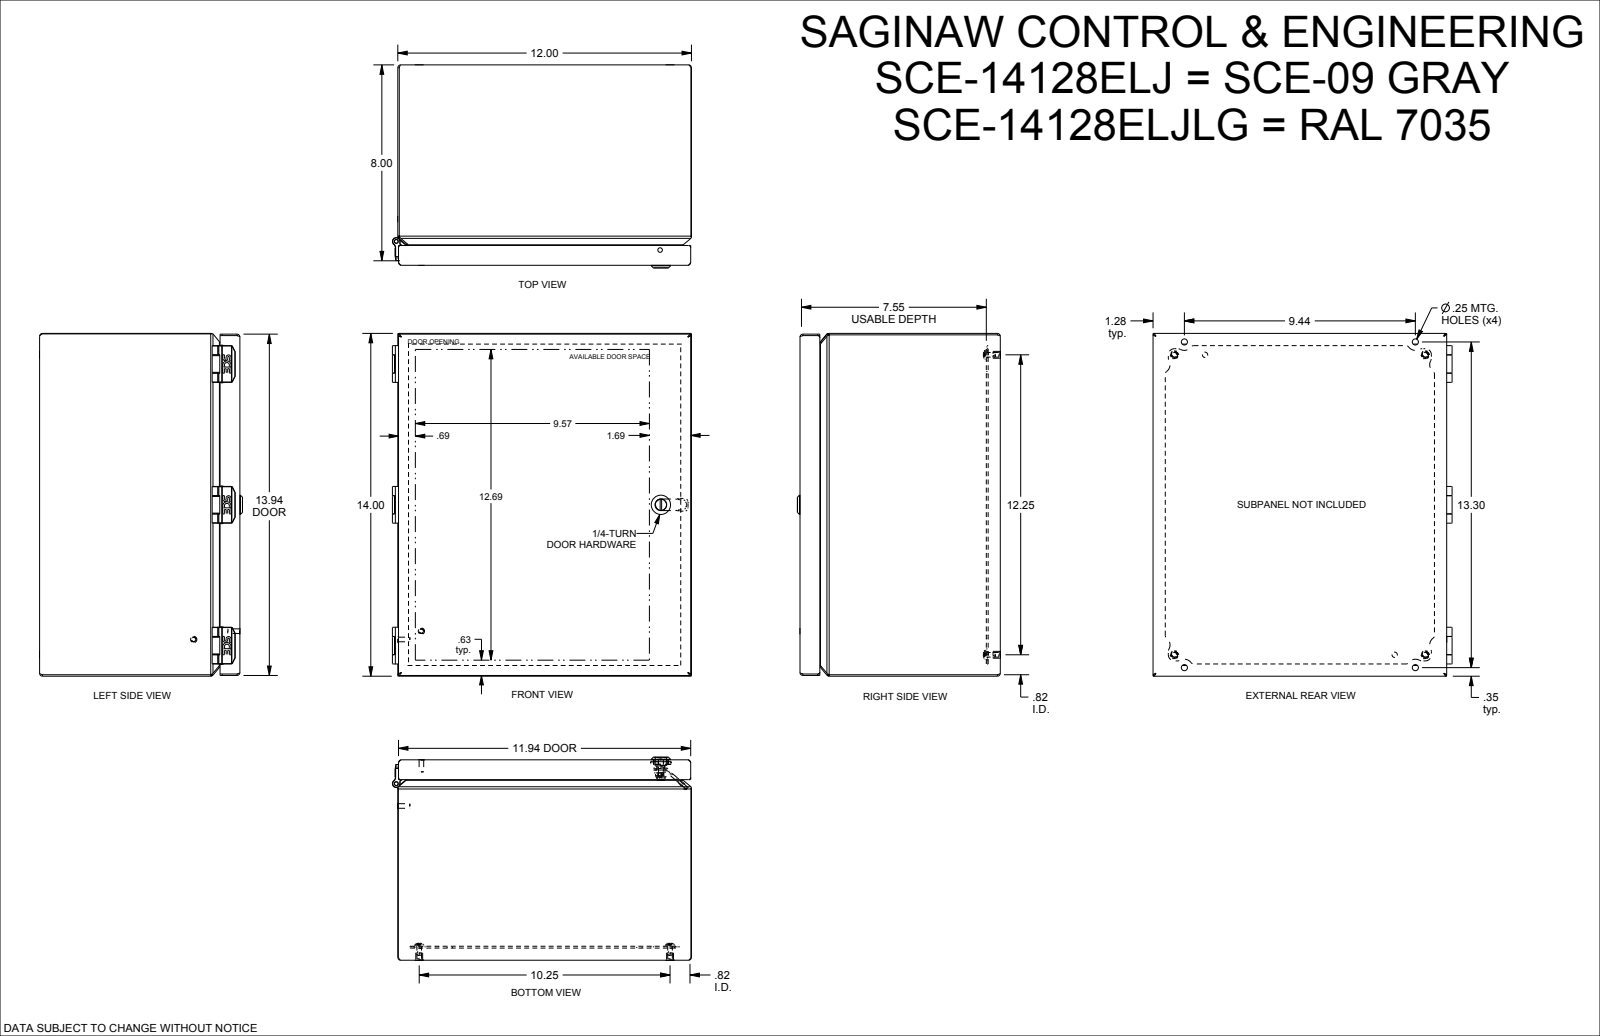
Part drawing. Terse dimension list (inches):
name: SCE-14128ELJ
written by: SolidWorks 2019 (AUTOMOTIVE_DESIGN)
unit: in
bodies: 35 solids, 1114 faces (406 planar, 387 cylindrical, 321 other)
size: 14 × 12.22 × 8.296
volume: 62.02 in³; area: 1 958 in²
holes: 4× ⌀0.19, 4× ⌀0.25, 4× ⌀0.284, 3× ⌀0.02, 3× ⌀0.1, 2× ⌀0.218, 2× ⌀0.266, 1× ⌀0.158, 1× ⌀0.196, 1× ⌀0.2, 1× ⌀0.239, 1× ⌀0.254
bosses: 6× ⌀0.188, 6× ⌀0.16, 4× ⌀0.373, 4× ⌀0.28, 3× ⌀0.26, 3× ⌀0.237, 3× ⌀0.23, 3× ⌀0.18
rounds: 40× R0.03, 31× R0.013, 16× R0.05, 13× R0.25, 12× R0.01, 12× R0.062, 11× R0.125, 10× R0.06
face distances: 0.059, 0.06, 11.941, 13.941, 8.185, 8.126, 8.125, 8.066, 0.571, 0.512
hole spacings: 10.25, 1.25, 1.25, 5.75, 6.136, 9, 9, 10.25
